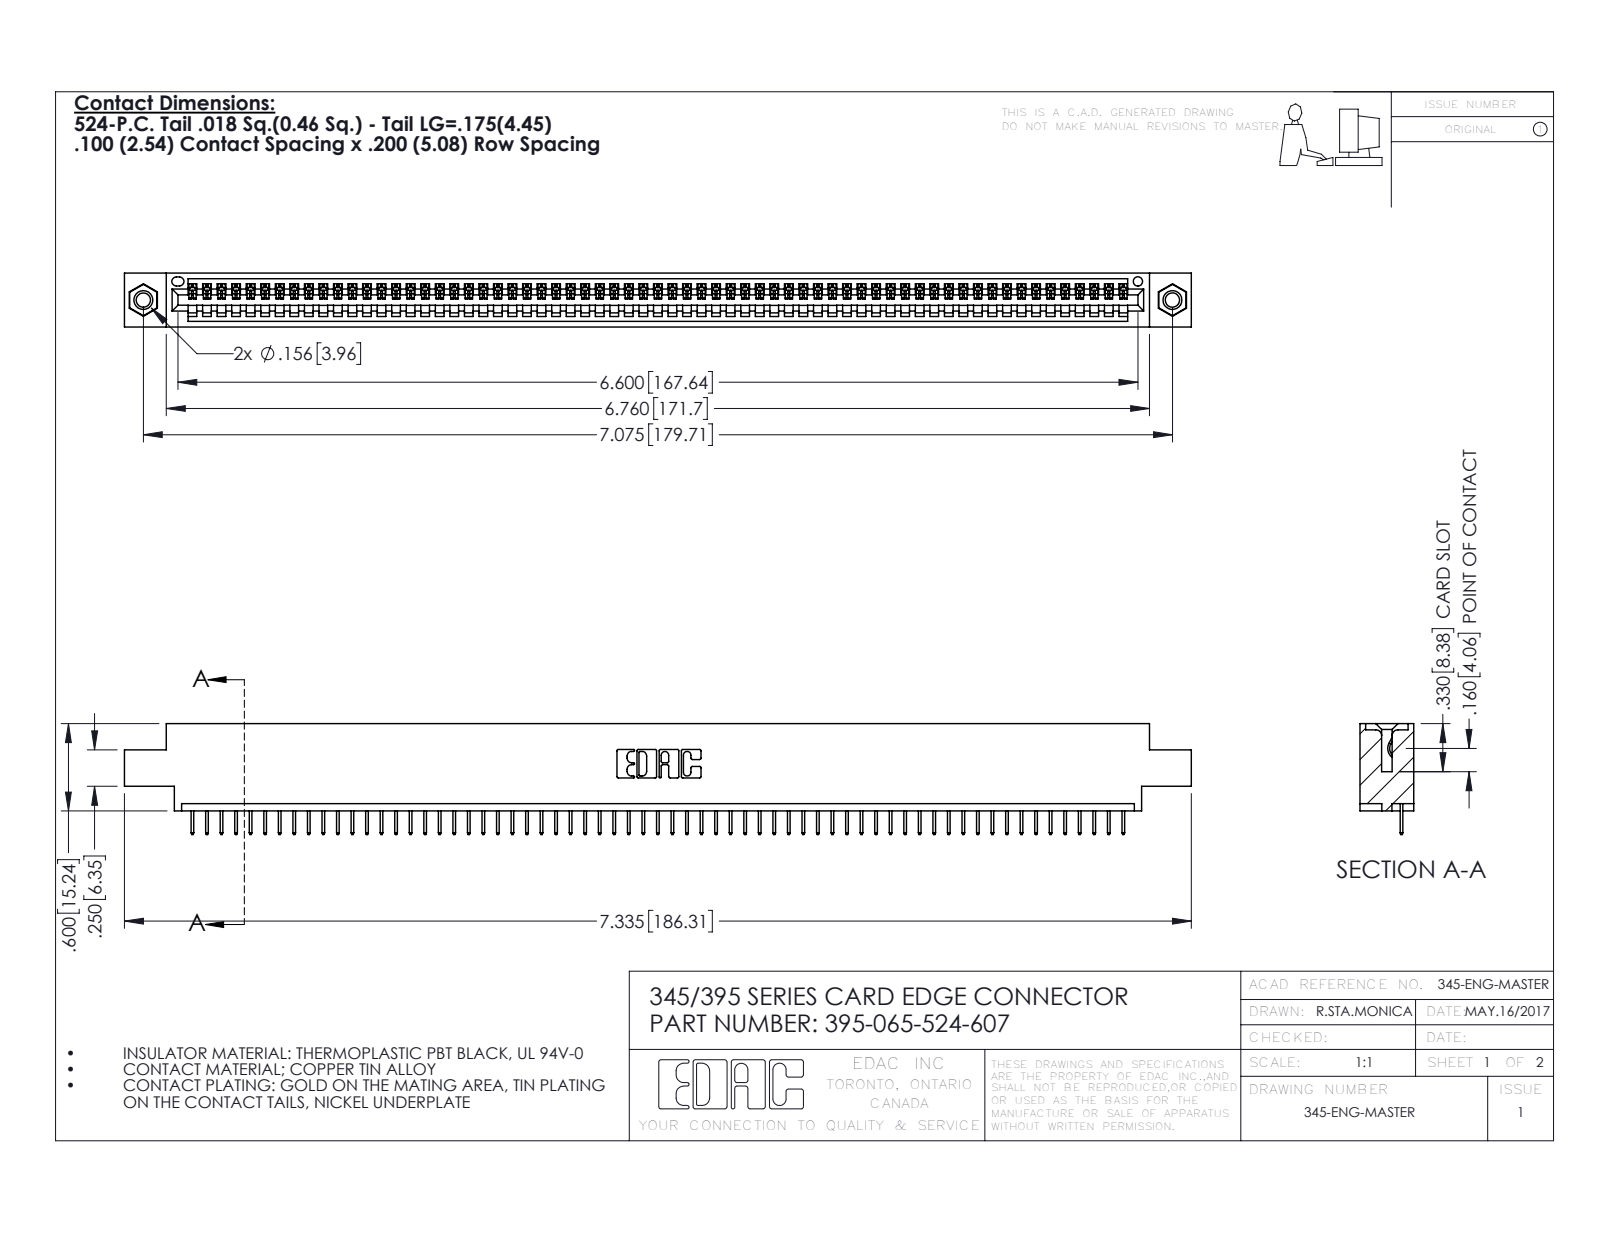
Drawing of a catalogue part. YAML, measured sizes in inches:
part_name: "345 Part_0.170 Offset - 0.156 Dia-TI; 345-250-001_345-250-005-103; 395-065-524-607; 345-292-001_345-293-124"
step_written_by: "SolidWorks 2016 (CONFIG_CONTROL_DESIGN)"
units: inches
bodies: {solids: 68, faces: 4220, planar: 3106, cylindrical: 1098, other: 16}
overall_size: [7.335, 0.762, 0.37]
volume: 1.068
surface_area: 35.51
round_holes:
  - {diameter: 0.098, count: 2}
  - {diameter: 0.125, count: 2}
  - {diameter: 0.156, count: 2}
  - {diameter: 0.064, count: 1}
round_bosses_or_shafts:
  - {diameter: 0.155, count: 2}
partial_cylinders:
  - {radius: 0.006, count: 130}
  - {radius: 0.01, count: 22}
  - {radius: 0.007, count: 6}
  - {radius: 0.031, count: 6}
  - {radius: 0.026, count: 3}
  - {radius: 0.031, count: 2}
  - {radius: 0.04, count: 2}
  - {radius: 0.014, count: 1}
face_to_face_distances: [0.072, 0.298, 0.37, 0.2, 0.098, 0.272, 0.025, 0.225, 0.072, 0.175]
hole_center_spacings: [0.27, 6.839, 7.075]
